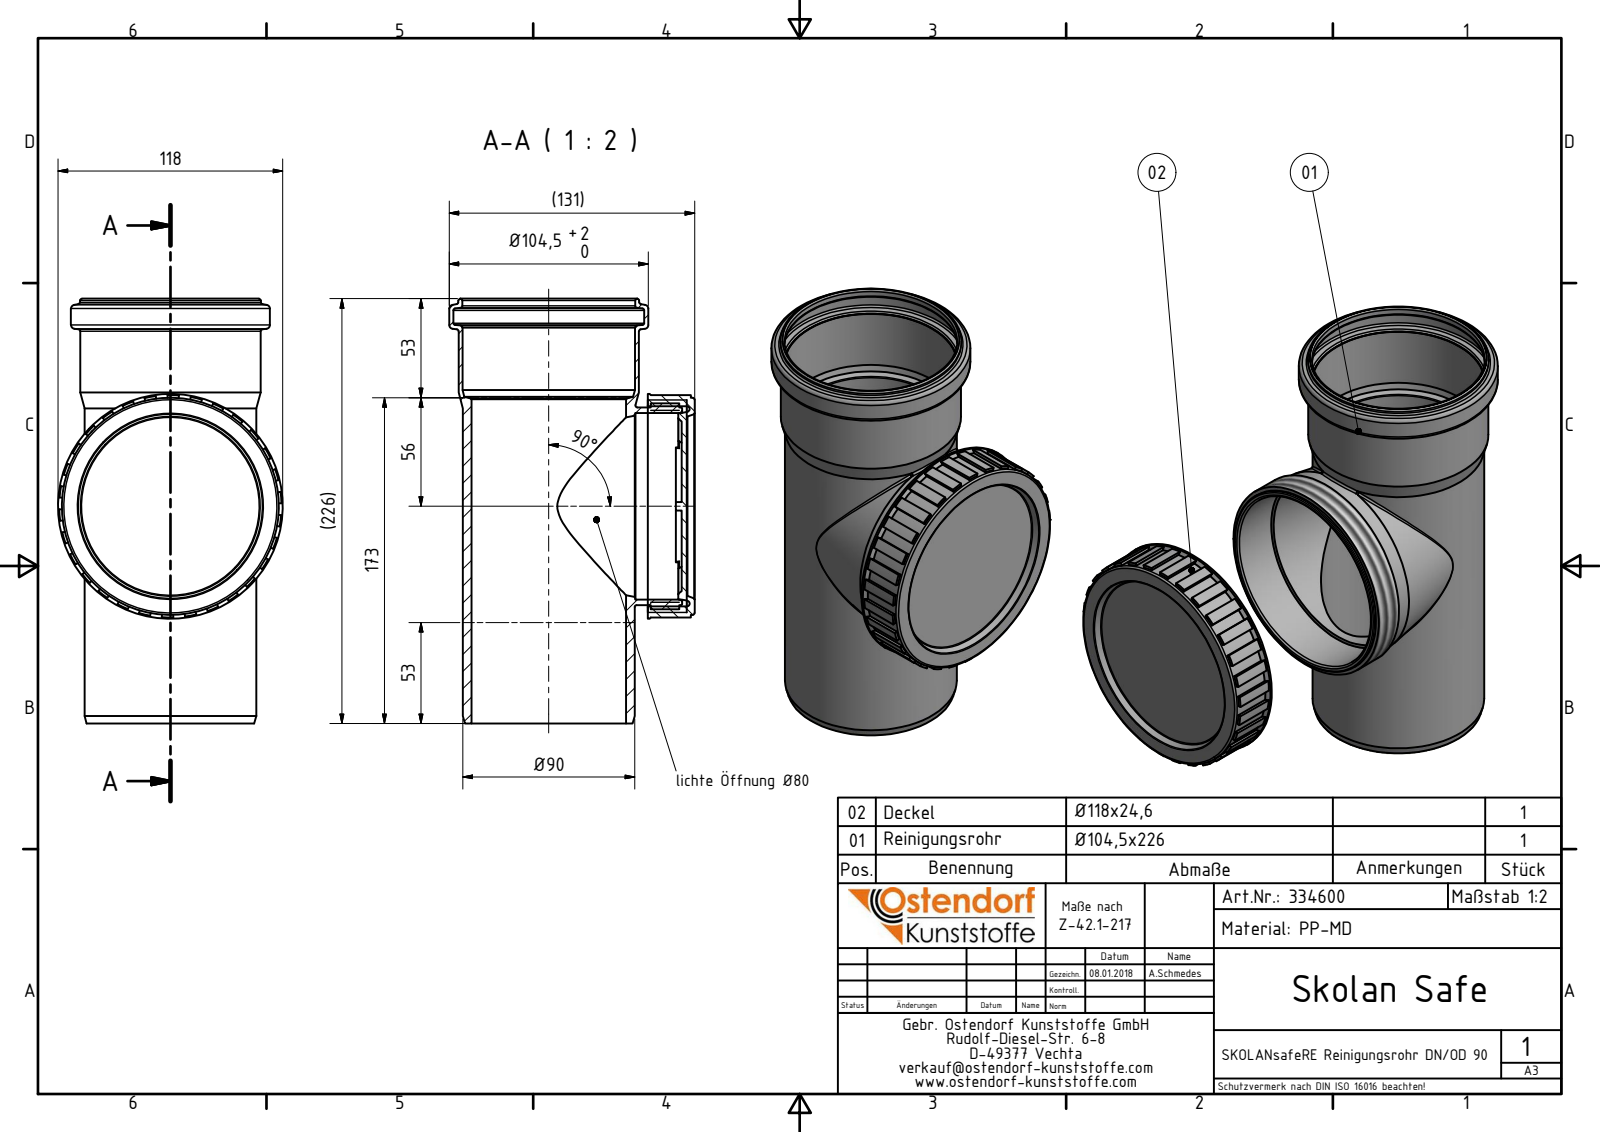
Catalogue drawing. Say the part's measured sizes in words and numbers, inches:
The part is named "334600 SKRE Reinigungsrohr DN_OD 90; 334600 SKRE Reinigungsrohr DN_OD 90 Deckel; 334600 SKOLANsafeRE Reinigungsrohr DN_OD 90". Its 3-D file was written by "Autodesk Inventor 2016 (AUTOMOTIVE_DESIGN)". It is 2 solids with 220 faces: 113 planar, 59 cylindrical and 48 other. Overall it measures 8.78 by 5.073 by 4.646 inches. Its volume is 20.8 cubic inches and its surface area 286.3 square inches. Round holes: 1 of diameter 3.197, 1 of diameter 3.563, 1 of diameter 3.575, 1 of diameter 3.858, 1 of diameter 3.949, 1 of diameter 4.134. Round bosses or shafts: 1 of diameter 4.646, 1 of diameter 4.488, 1 of diameter 4.252, 1 of diameter 4.114, 1 of diameter 4.085, 1 of diameter 3.74, 1 of diameter 3.728, 1 of diameter 3.551. Partial cylindrical surfaces (rounded edges, fillets, slot ends): 4 of radius 0.02, 4 of radius 0.059, 1 of radius 2.299. The main face-to-face distances are 0.11, 0.157, 0.268, 0.969, 0.811, 0.701, 0.059, 0.65, 0.181, 0.079.
